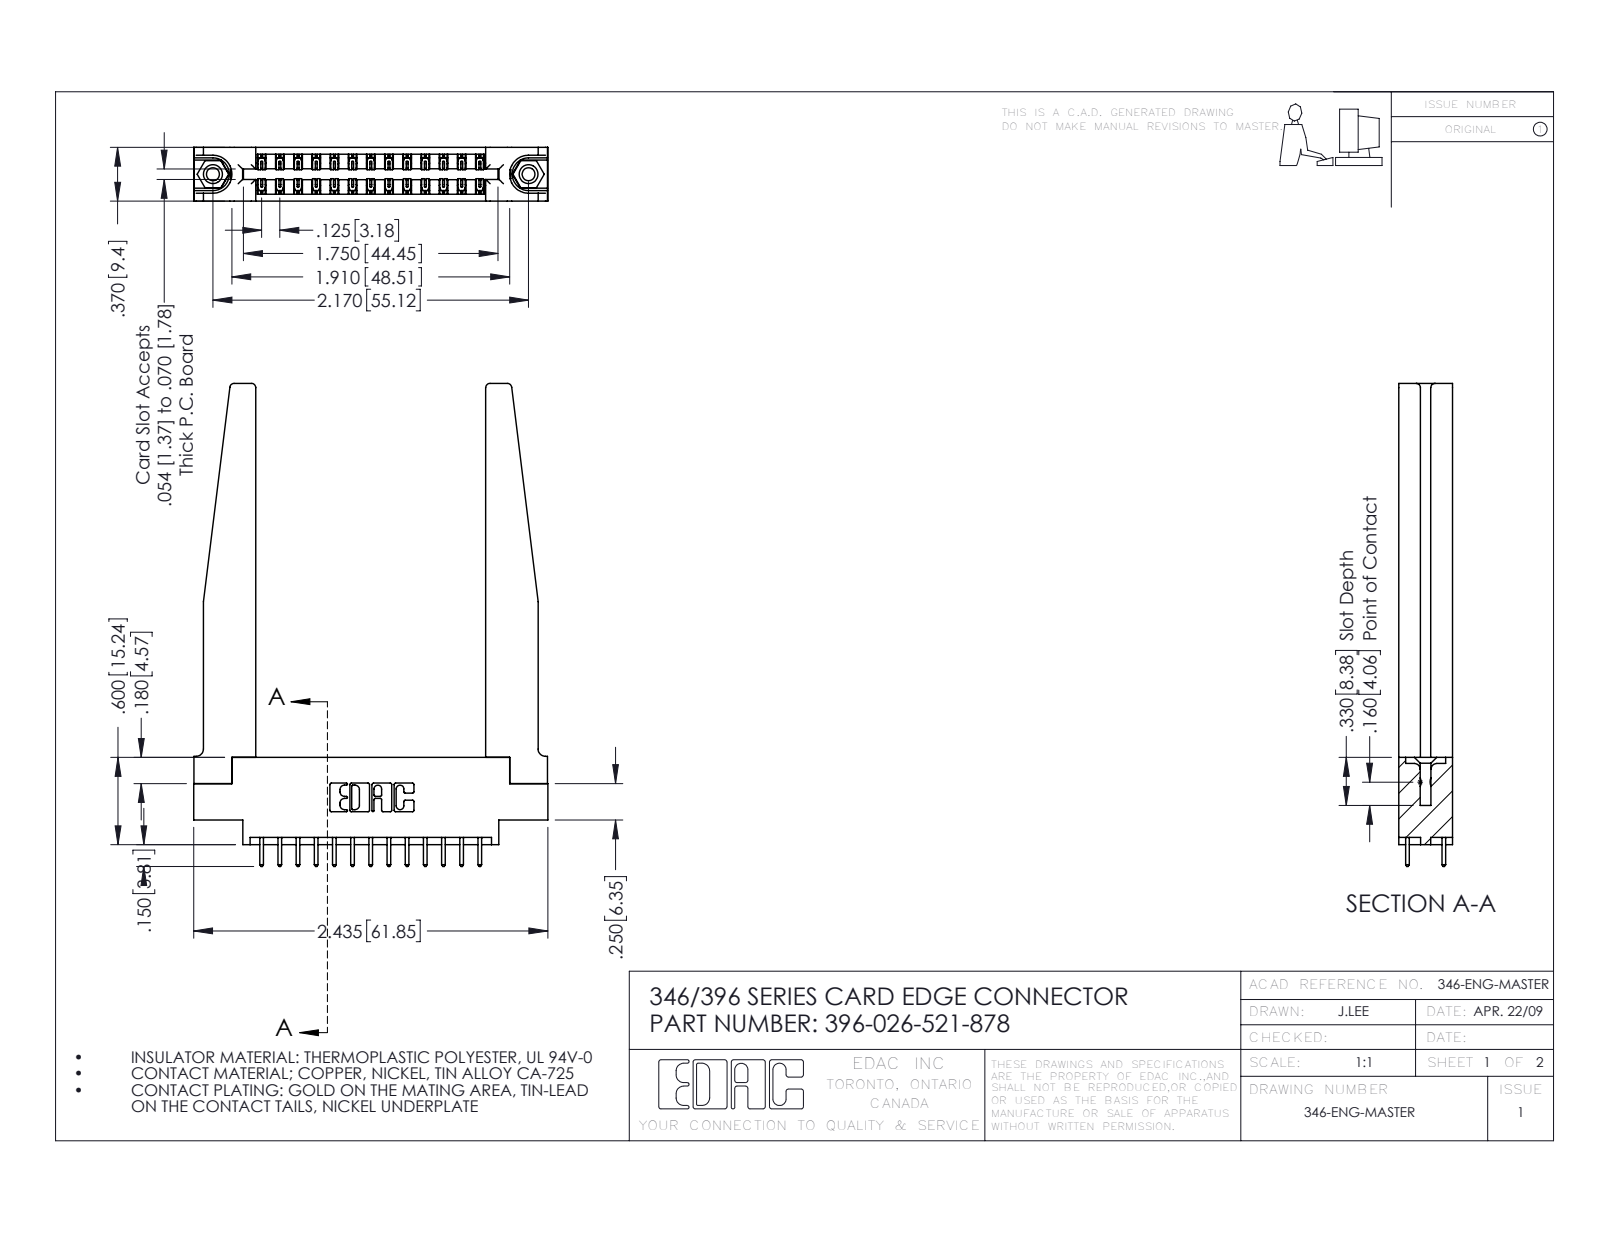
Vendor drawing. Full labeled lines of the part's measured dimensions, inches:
Part name (STEP PRODUCT): 346-220-078_345-220-078; 345-292-001_345-293-121; 396-026-521-878; 346 Part_0.170 Offset - 0.156 Dia-TH (+1 more)
STEP written by: SolidWorks 2016 (CONFIG_CONTROL_DESIGN)
Units: inches
Bodies: 31 solids, 1712 faces (1132 planar, 528 cylindrical, 52 other)
Overall size (bounding box): 3.32 × 2.435 × 0.37
Volume: 0.766 in³ · Surface area: 21.61 in²
Round holes (diameter × count): ⌀0.089 ×2, ⌀0.125 ×2, ⌀0.156 ×2, ⌀0.064 ×1
Round bosses / shafts (diameter × count): ⌀0.155 ×2
Partial cylindrical surfaces — rounded edges, fillets, slot ends (radius × count): R0.006 ×39, R0.01 ×26, R0.01 ×22, R0.03 ×8, R0.007 ×6, R0.031 ×6, R0.026 ×3, R0.014 ×2
Main face-to-face distances: 0.37, 0.15, 0.072, 0.148, 0.048, 0.322, 0.25, 0.102, 0.22, 0.173
Hole centre spacings: 0.246, 1.964, 2.17
